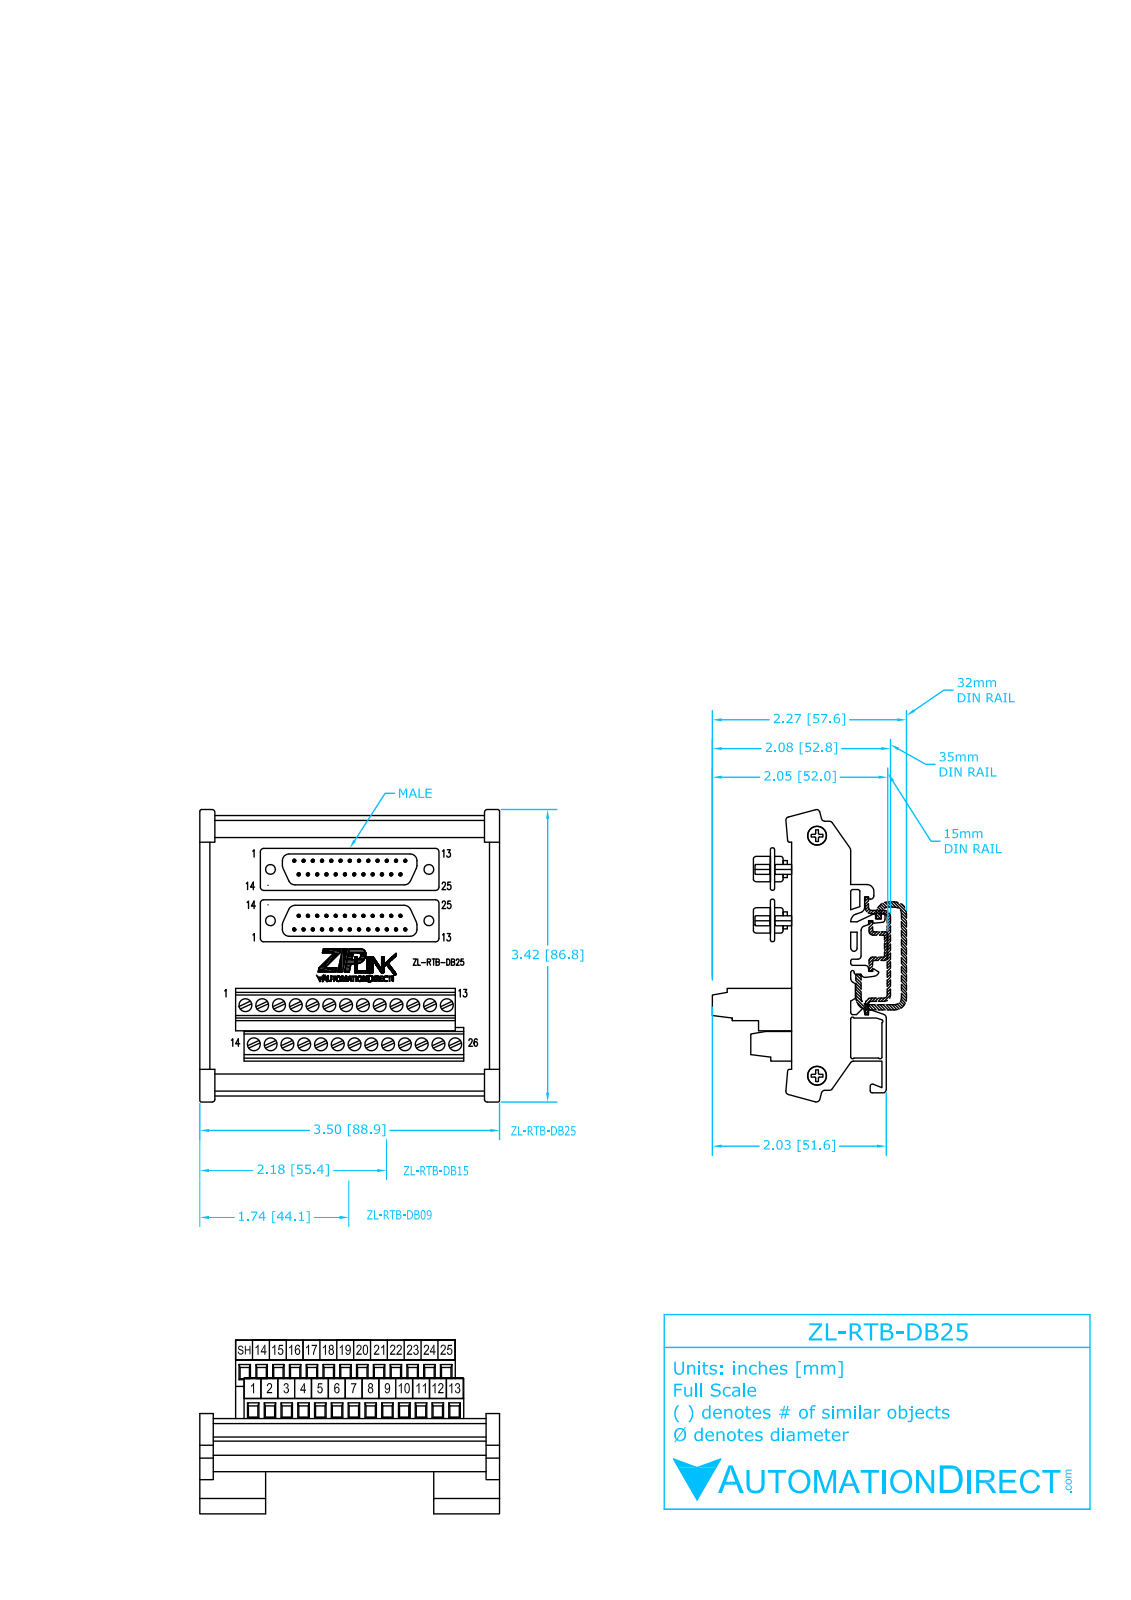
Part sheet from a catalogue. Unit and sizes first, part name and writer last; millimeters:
Units: millimetres
Overall size (bounding box): 90.3 × 86.9 × 51.6
Round holes (diameter × count): ⌀3.8 ×26, ⌀1.4 ×24, ⌀2.3 ×4, ⌀5.7 ×2, ⌀1.4 ×1
Round bosses / shafts (diameter × count): ⌀0.9 ×25, ⌀5.2 ×2
Partial cylindrical surfaces — rounded edges, fillets, slot ends (radius × count): R0.4 ×41, R0.8 ×10, R1.5 ×8, R2 ×8, R2.5 ×8
Main face-to-face distances: 16, 0.8, 16.7, 88.9, 6.9, 0.5, 6.1, 22.8, 34.3, 27.4
Hole centre spacings: 2.5, 5.1, 7.6, 10.2, 12.7, 15.2, 3.2, 3.4
Volume: 148 500 mm³ · Surface area: 42 540 mm²
Bodies: 1 solid, 1083 faces (758 planar, 317 cylindrical, 8 other)
Part name (STEP PRODUCT): ZL-RTB-DB25
STEP written by: SolidWorks 2014 (AUTOMOTIVE_DESIGN)
